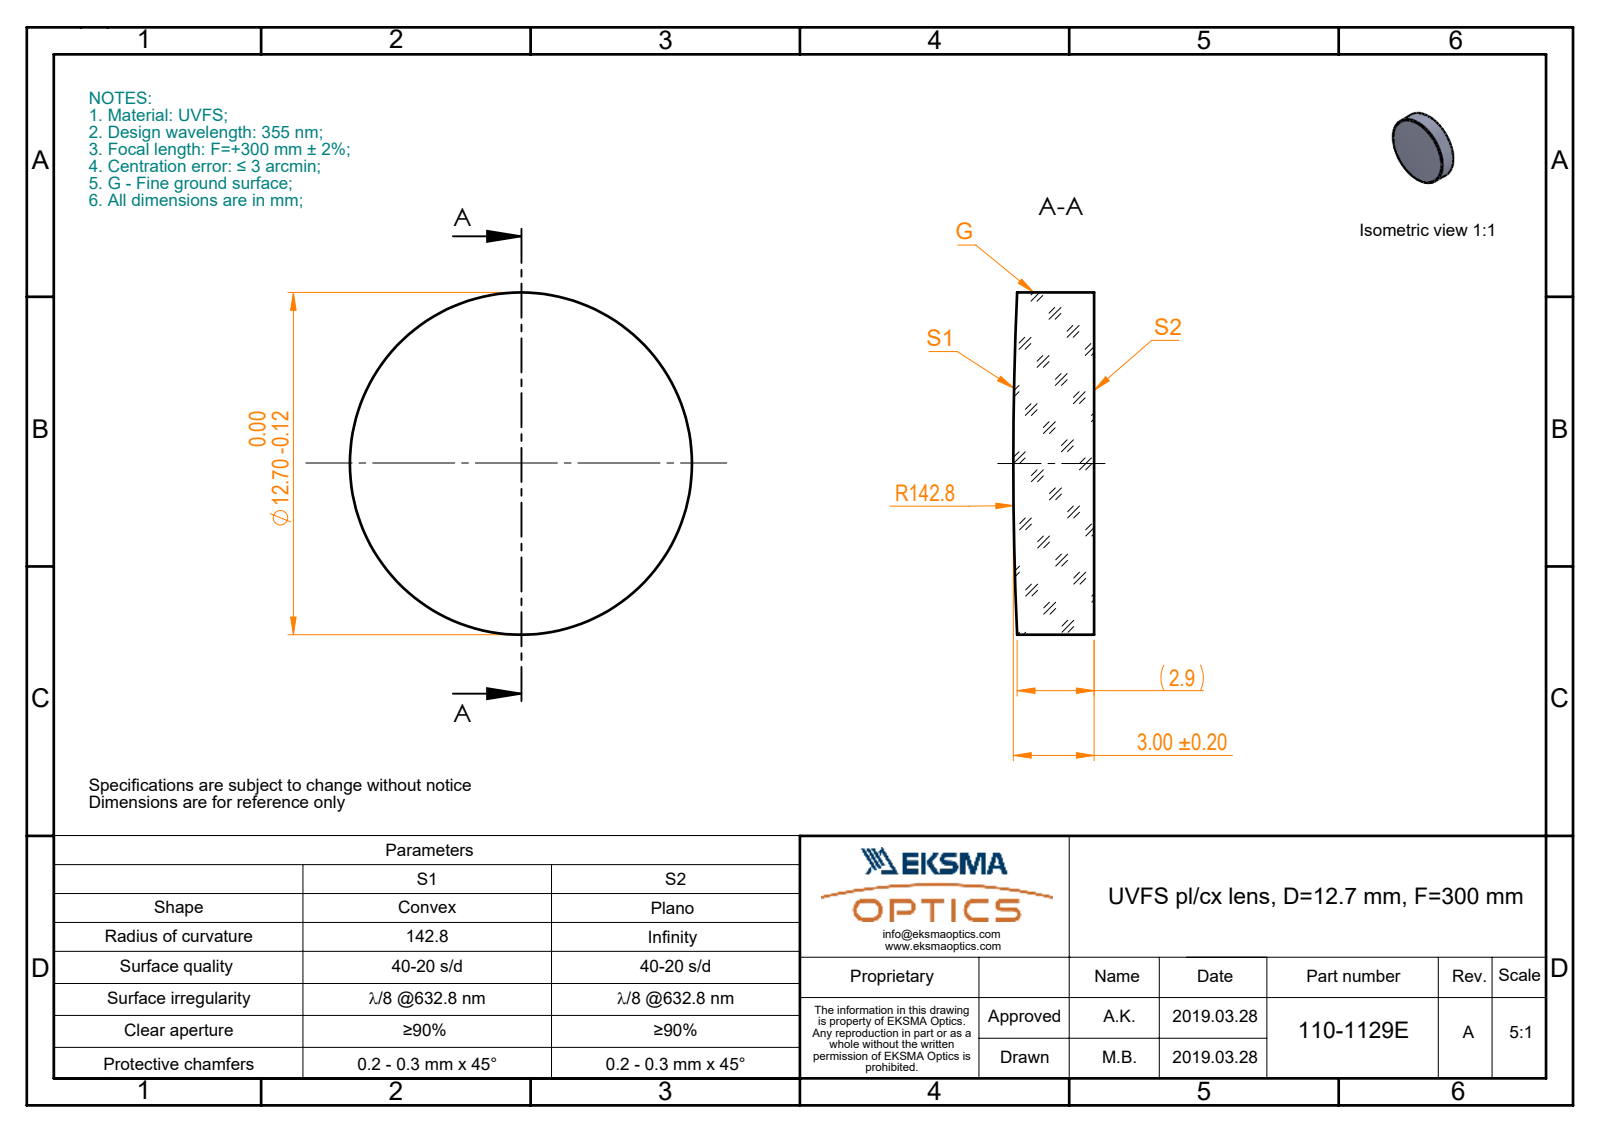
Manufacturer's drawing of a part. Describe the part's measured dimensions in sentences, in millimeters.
The part is named "110-1129E UVFS pl-cx 12.7 F300". Its 3-D file was written by "SolidWorks 2017 (CONFIG_CONTROL_DESIGN)". It is 1 solid with 5 faces: 1 planar, 2 cylindrical and 2 other. Overall it measures 12.7 by 12.7 by 3 millimeters. Its volume is 371 cubic millimeters and its surface area 367 square millimeters. Round bosses or shafts: 1 of diameter 12.7.
